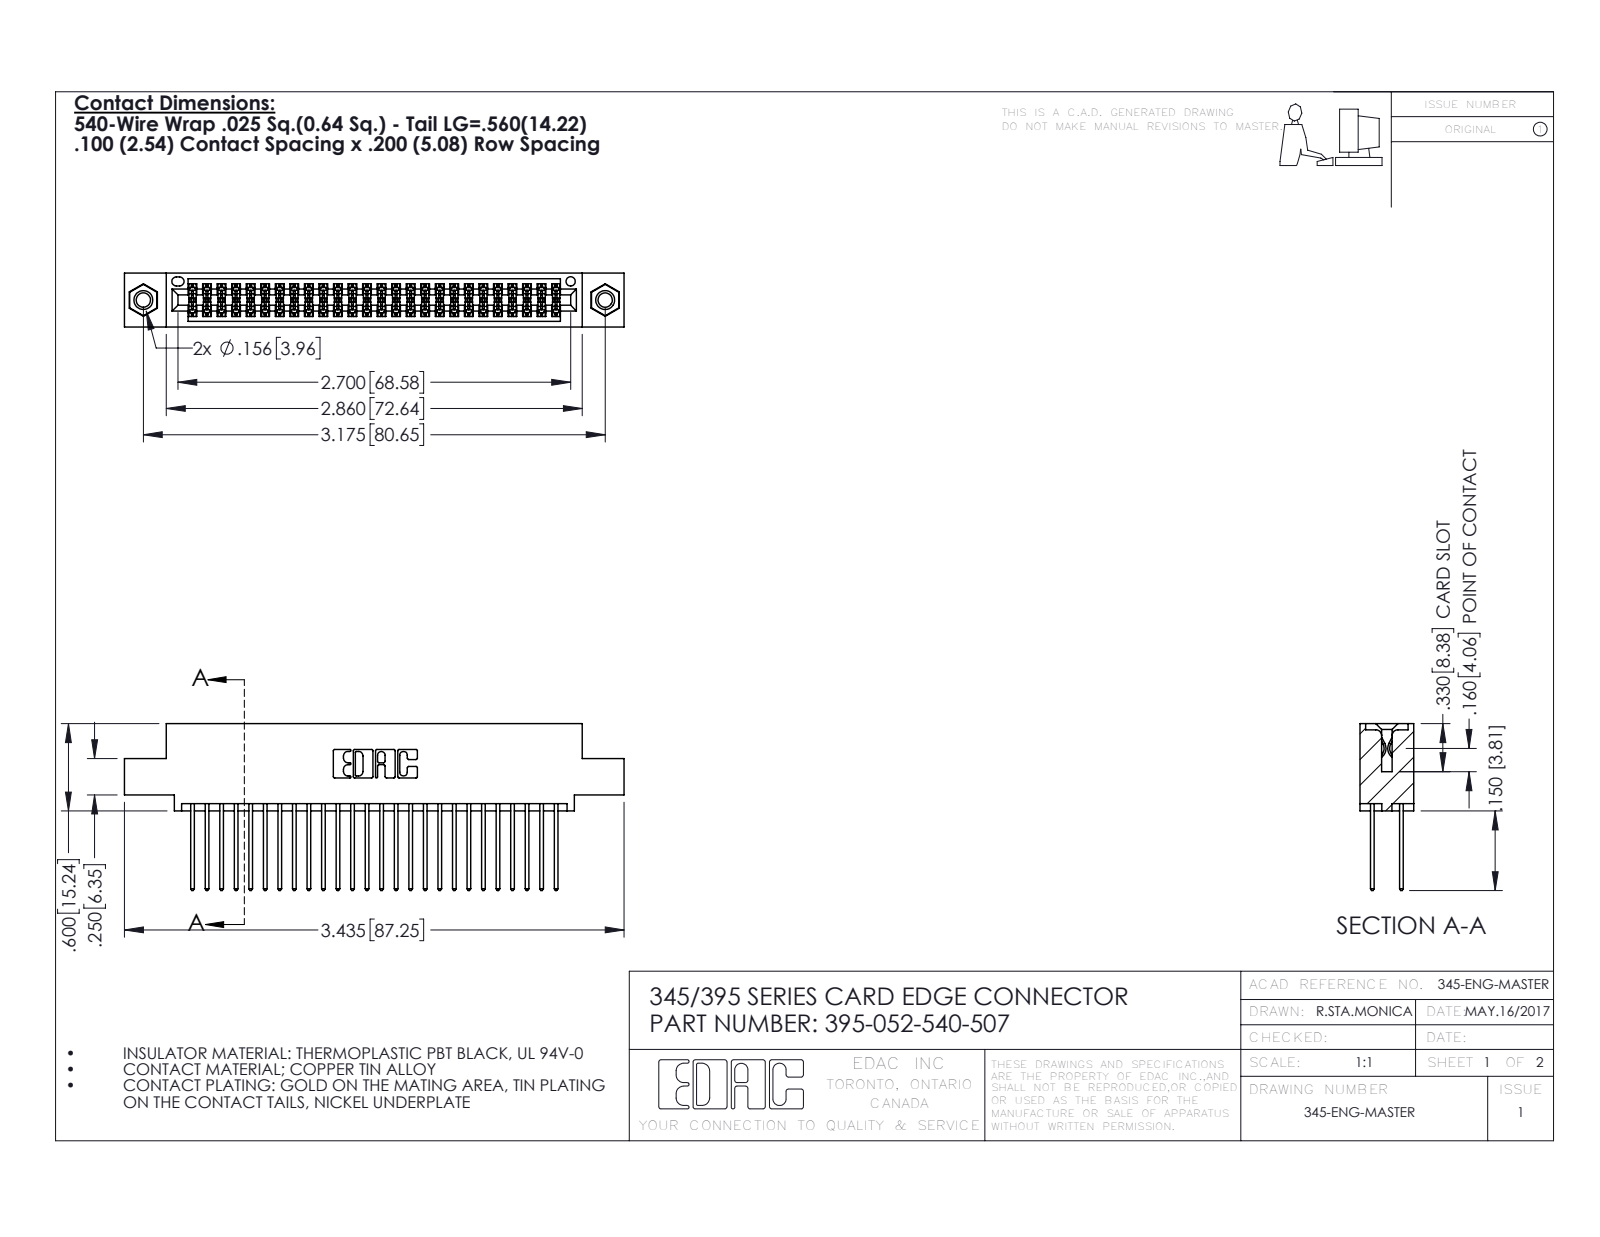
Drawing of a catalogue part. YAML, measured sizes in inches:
part_name: "345-250-001_345-250-005-103; 395-052-540-507; 345-292-001_345-293-140; 345 Part_0.110 Offset - 0.156 Dia-TI"
step_written_by: "SolidWorks 2016 (CONFIG_CONTROL_DESIGN)"
units: inches
bodies: {solids: 55, faces: 2790, planar: 1832, cylindrical: 942, other: 16}
overall_size: [3.435, 1.147, 0.37]
volume: 0.515
surface_area: 20.46
round_holes:
  - {diameter: 0.098, count: 2}
  - {diameter: 0.125, count: 2}
  - {diameter: 0.156, count: 2}
  - {diameter: 0.064, count: 1}
round_bosses_or_shafts:
  - {diameter: 0.155, count: 2}
partial_cylinders:
  - {radius: 0.006, count: 78}
  - {radius: 0.01, count: 52}
  - {radius: 0.01, count: 22}
  - {radius: 0.007, count: 6}
  - {radius: 0.031, count: 6}
  - {radius: 0.026, count: 3}
  - {radius: 0.014, count: 2}
  - {radius: 0.019, count: 2}
face_to_face_distances: [0.072, 0.298, 0.2, 0.098, 0.272, 0.025, 0.37, 0.225, 0.175, 0.149]
hole_center_spacings: [0.27, 2.94, 3.175]
